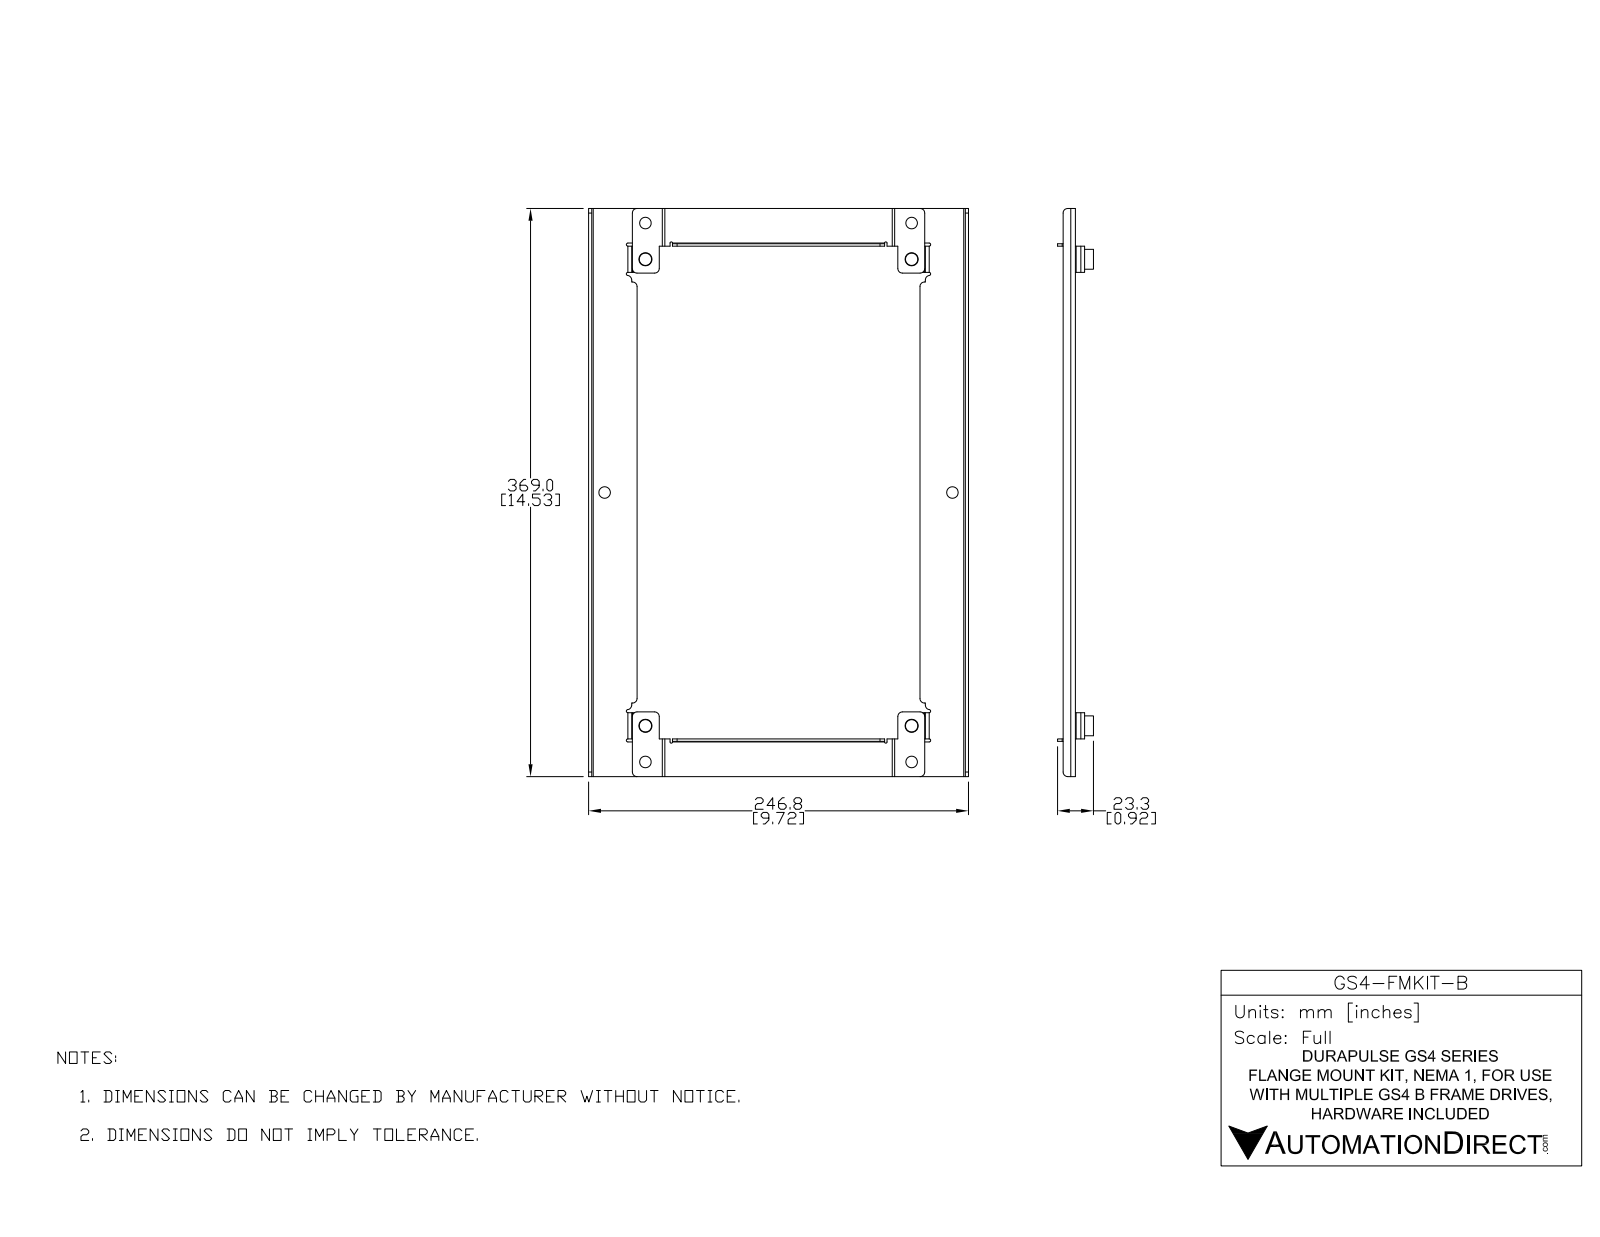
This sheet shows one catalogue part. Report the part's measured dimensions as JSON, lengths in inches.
{"part_name": "GS4-FMKIT-B", "step_written_by": "SolidWorks 2015 (AUTOMOTIVE_DESIGN)", "units": "inches", "bodies": {"solids": 0, "faces": 278, "planar": 186, "cylindrical": 0, "other": 92}, "overall_size": [14.528, 9.717, 0.996], "face_to_face_distances": [0.079, 0.063, 0.016, 9.638, 0.142, 0.236, 0.315, 12.661, 9.559, 9.717]}
